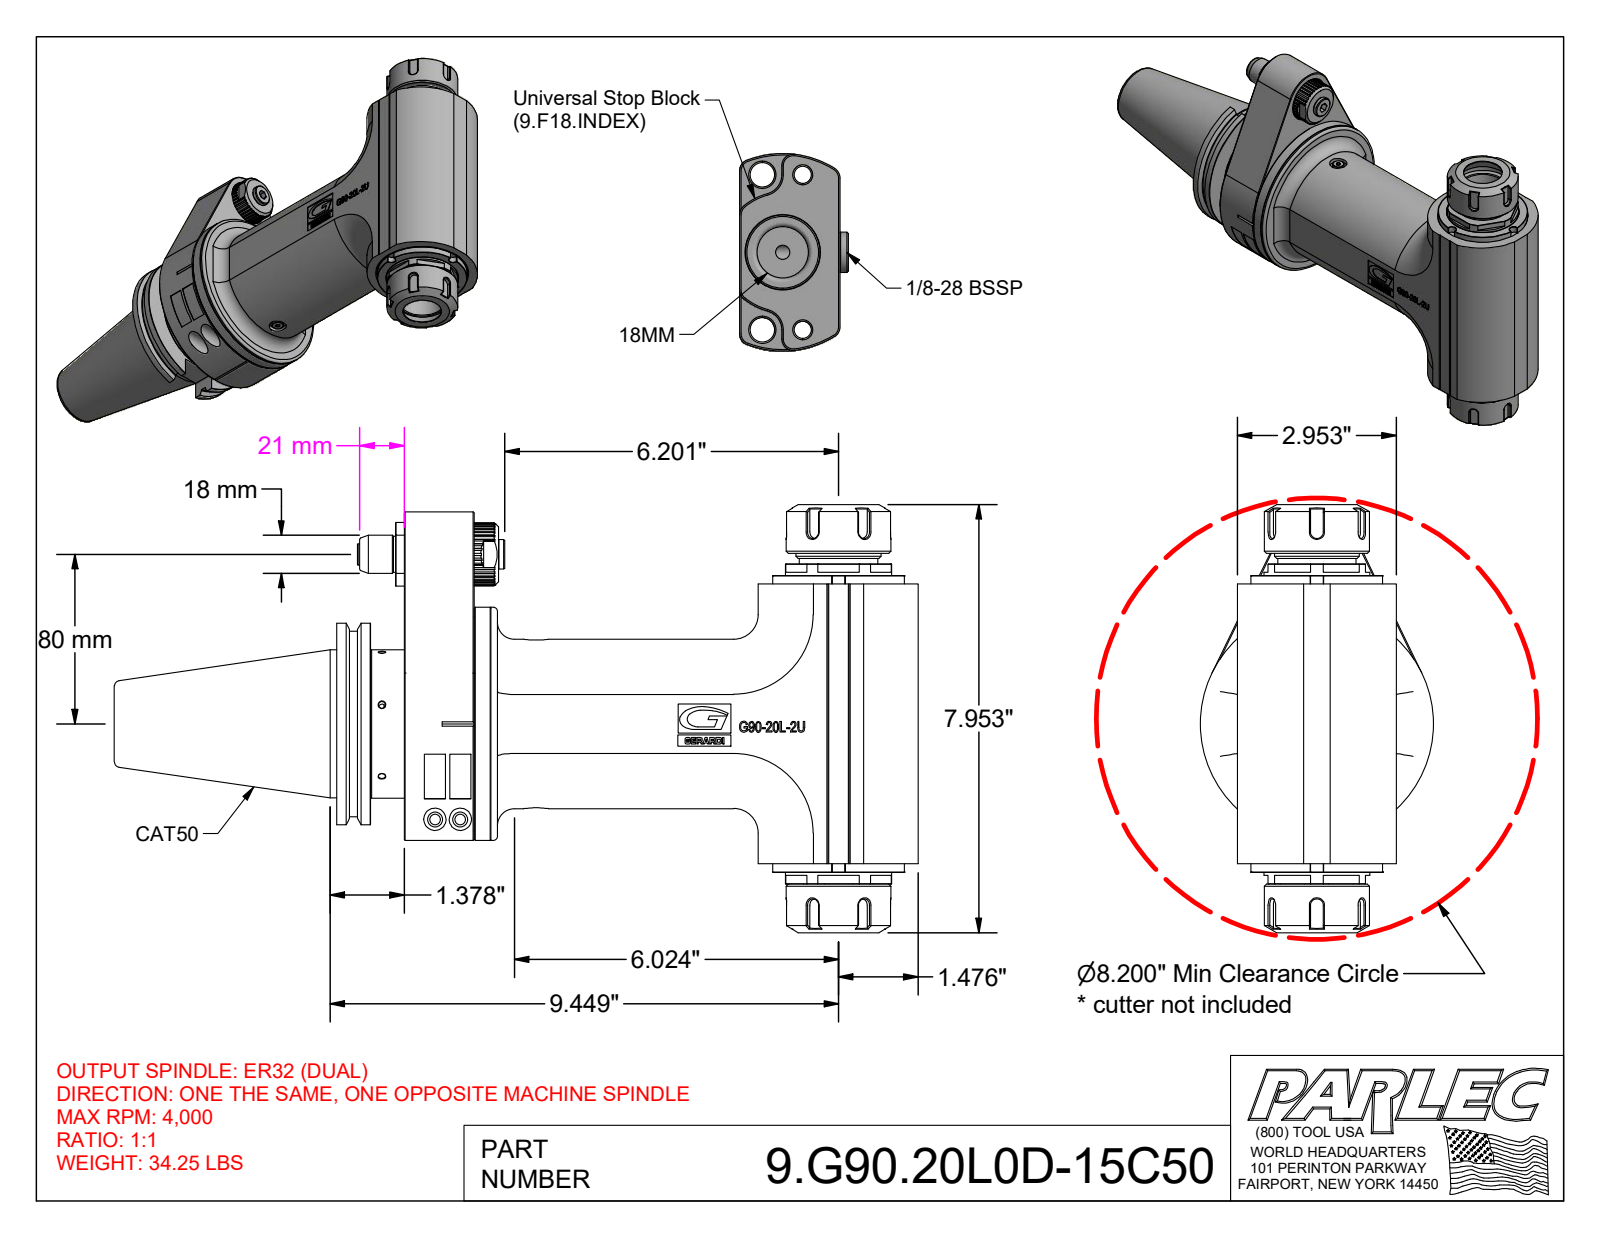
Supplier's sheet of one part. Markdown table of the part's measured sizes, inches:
| quantity | value |
| --- | --- |
| part name | 9.G90.20L0D-15C50; G90-20LD |
| STEP written by | Autodesk Inventor 2020 (AUTOMOTIVE_DESIGN) |
| units | inches |
| bodies | 3 solids, 1534 faces (700 planar, 318 cylindrical, 516 other) |
| overall size | 14.933 × 7.953 × 4.331 |
| volume | 99.49 in³ |
| surface area | 488.1 in² |
| round holes (diameter × count) | 0.13 × 9, 0.197 × 9, 0.118 × 8, 0.335 × 4, 0.165 × 3, 0.236 × 3, 0.157 × 2, 0.276 × 2, 0.362 × 2, 0.413 × 2, 0.472 × 2, 0.512 × 2 |
| round bosses / shafts (diameter × count) | 1.378 × 2, 0.504 × 2, 0.354 × 2, 0.228 × 2, 4.331 × 1, 4.016 × 1, 3.875 × 1, 3.593 × 1 |
| partial cylindrical surfaces (radius × count) | 0.059 × 16, 0.118 × 14, 0.085 × 2, 0.315 × 2, 1.575 × 2, 0.079 × 1, 0.115 × 1, 0.151 × 1 |
| main face-to-face distances | 0.626, 2.953, 0.197, 1.299, 0.118, 1.181, 0.02, 0.177, 1.925, 0.744 |
| hole center spacings | 0.505, 0.713, 1.87, 3.239, 0.283, 0.484, 0.885, 0.969 |
